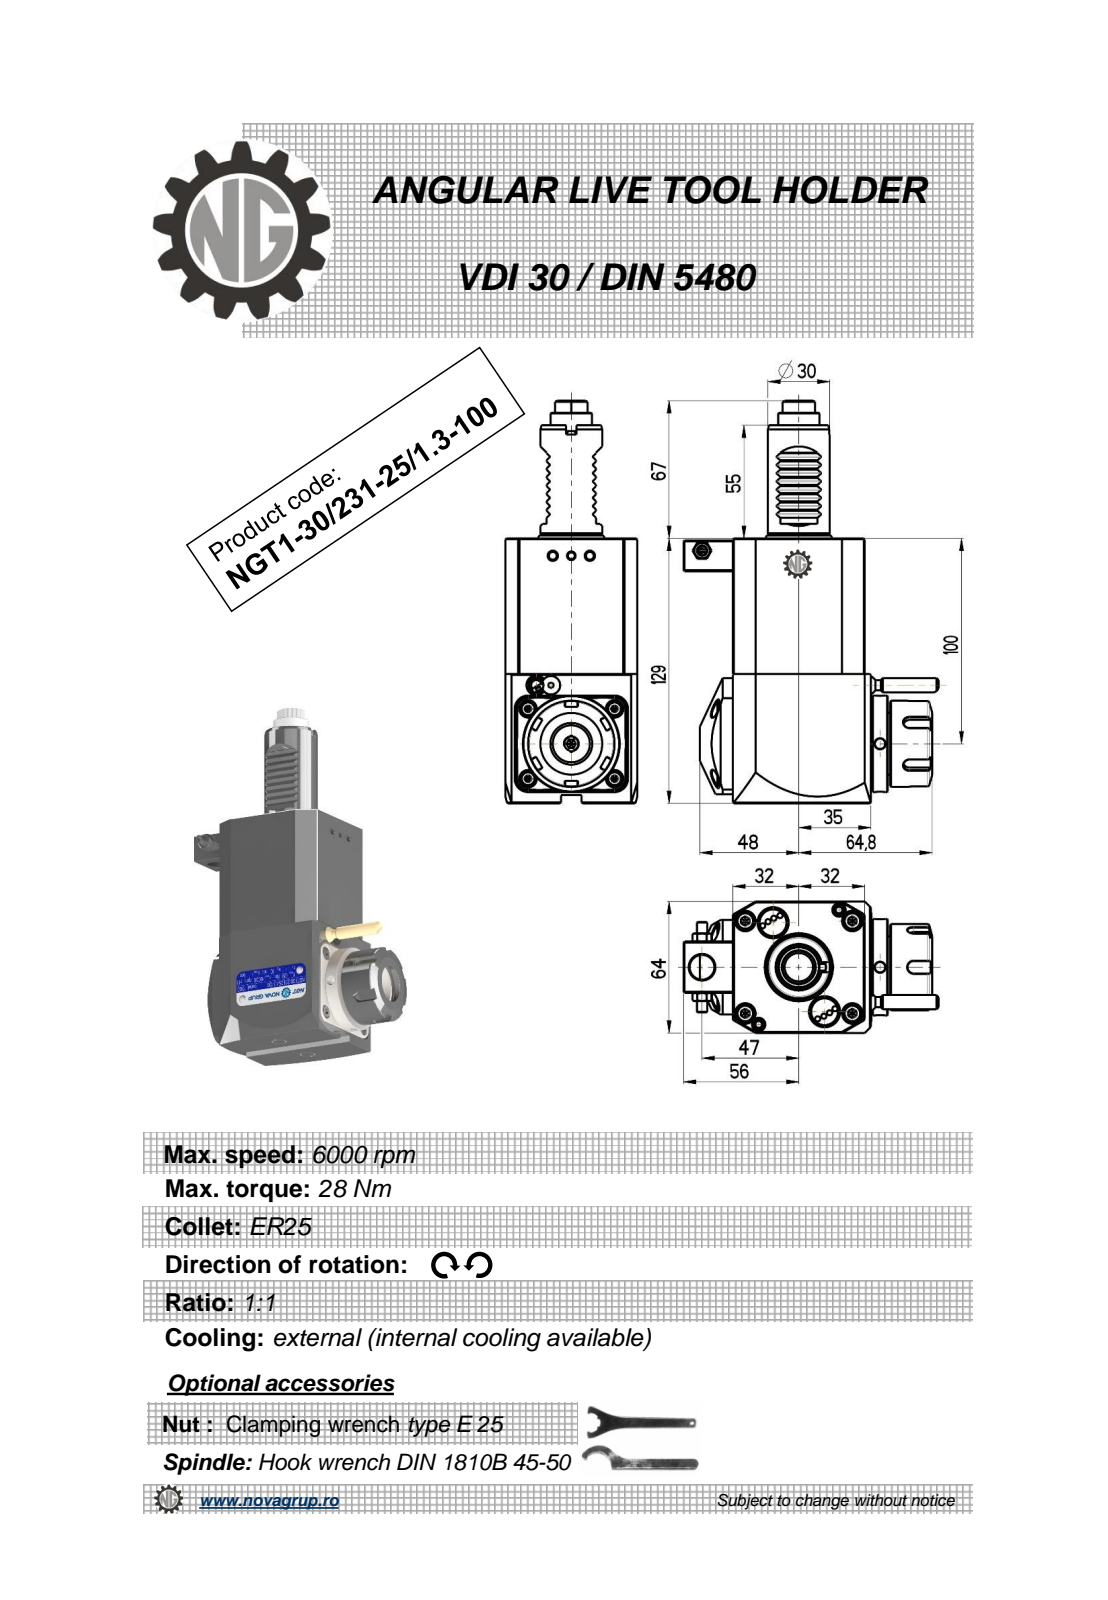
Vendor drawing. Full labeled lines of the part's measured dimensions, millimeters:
Part name (STEP PRODUCT): NGT1_30_231_25_1_3_100
STEP written by: PRO/ENGINEER BY PARAMETRIC TECHNOLOGY CORPORATION, 2010280 (CONFIG_CONTROL_DESIGN)
Units: millimetres
Bodies: 1 solid, 562 faces (227 planar, 165 cylindrical, 170 other)
Overall size (bounding box): 196 × 123.83 × 64
Volume: 634 742 mm³ · Surface area: 58 863 mm²
Round holes (diameter × count): ⌀5 ×2, ⌀2.5 ×1, ⌀3 ×1, ⌀4.2 ×1, ⌀9.5 ×1, ⌀12 ×1, ⌀20.3 ×1
Round bosses / shafts (diameter × count): ⌀8.96 ×2, ⌀5 ×2, ⌀47 ×1, ⌀42 ×1, ⌀35 ×1, ⌀30 ×1, ⌀20 ×1, ⌀7 ×1
Partial cylindrical surfaces — rounded edges, fillets, slot ends (radius × count): R1.98 ×36, R0.3 ×16, R0.26 ×12, R3 ×5, R3.5 ×4, R160 ×2, R7.08 ×1, R7.92 ×1
Main face-to-face distances: 64, 129, 76.42, 0.5, 67.2, 3.2, 67, 7.5, 8, 3
Hole centre spacings: 33.19, 65.25, 86.45, 91.5, 127.71
